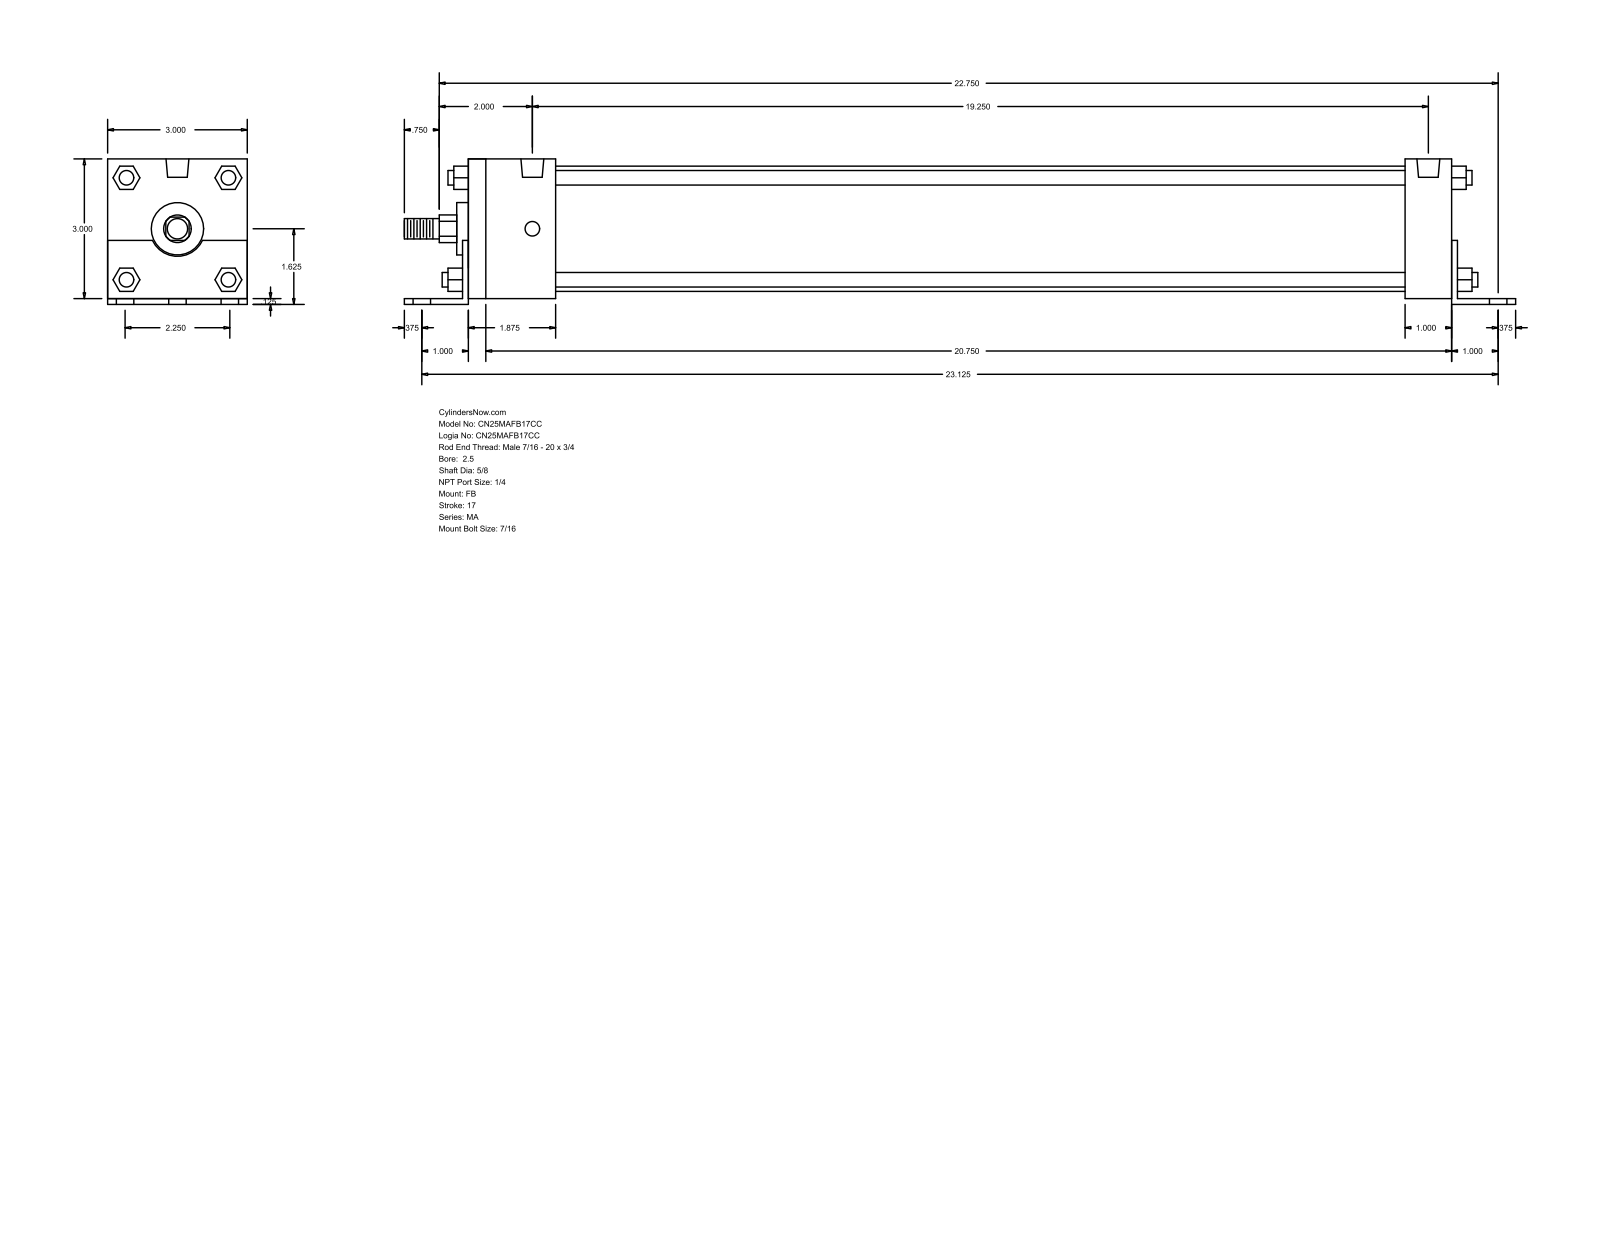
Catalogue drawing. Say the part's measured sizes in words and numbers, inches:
The part is named "MA_FB__0250_0.625". Its 3-D file was written by "GSSL Pune (CONFIG_CONTROL_DESIGN)". It is 0 solids with 140 faces: 105 planar, 35 cylindrical and 0 other. Overall it measures 23.875 by 3.125 by 3 inches. Round holes: 6 of diameter 0.437, 4 of diameter 0.313, 2 of diameter 0.492. Round bosses or shafts: 4 of diameter 0.313, 1 of diameter 2.69, 1 of diameter 1.125, 1 of diameter 0.625, 1 of diameter 0.437. Partial cylindrical surfaces (rounded edges, fillets, slot ends): 1 of radius 0.297, 1 of radius 0.593. The main face-to-face distances are 3, 0.125, 3.125, 21.125, 21.375, 0.125, 21.25, 1.875, 1, 21.25. The hole center spacings are 1.125, 23.152, 23.125, 1.875, 2.25, 2.628, 19.25, 20.78.
